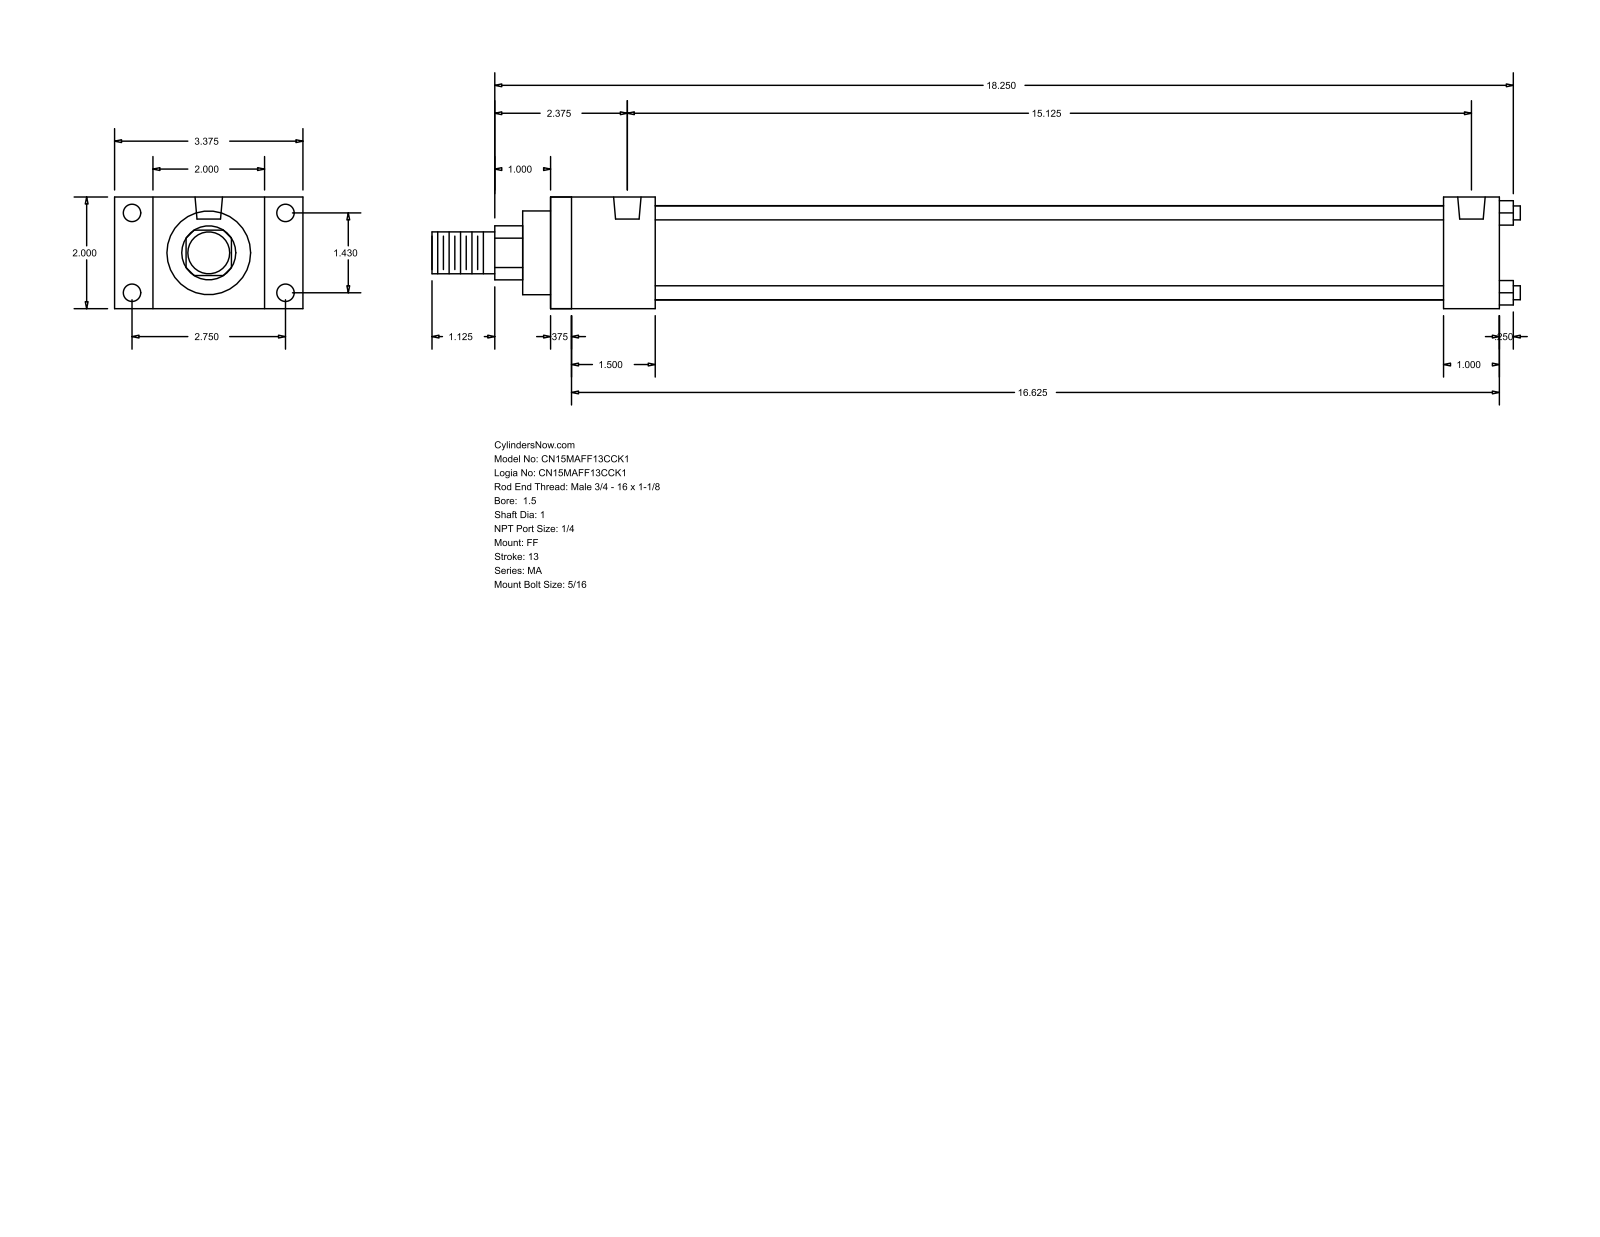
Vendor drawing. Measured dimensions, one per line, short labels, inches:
name: MA_FF__0150_1
written by: GSSL Pune (CONFIG_CONTROL_DESIGN)
unit: in
bodies: 0 solids, 92 faces (64 planar, 28 cylindrical, 0 other)
size: 19.5 × 3.375 × 2
holes: 8× ⌀0.313, 2× ⌀0.492
bosses: 4× ⌀0.25, 1× ⌀1.69, 1× ⌀1.5, 1× ⌀1, 1× ⌀0.75
rounds: 1× R0.484
face distances: 2, 17, 0.375, 16.625, 1, 1.875, 16, 1.5, 15.625, 14.125
hole spacings: 1.43, 2.75, 3.099, 15.125
